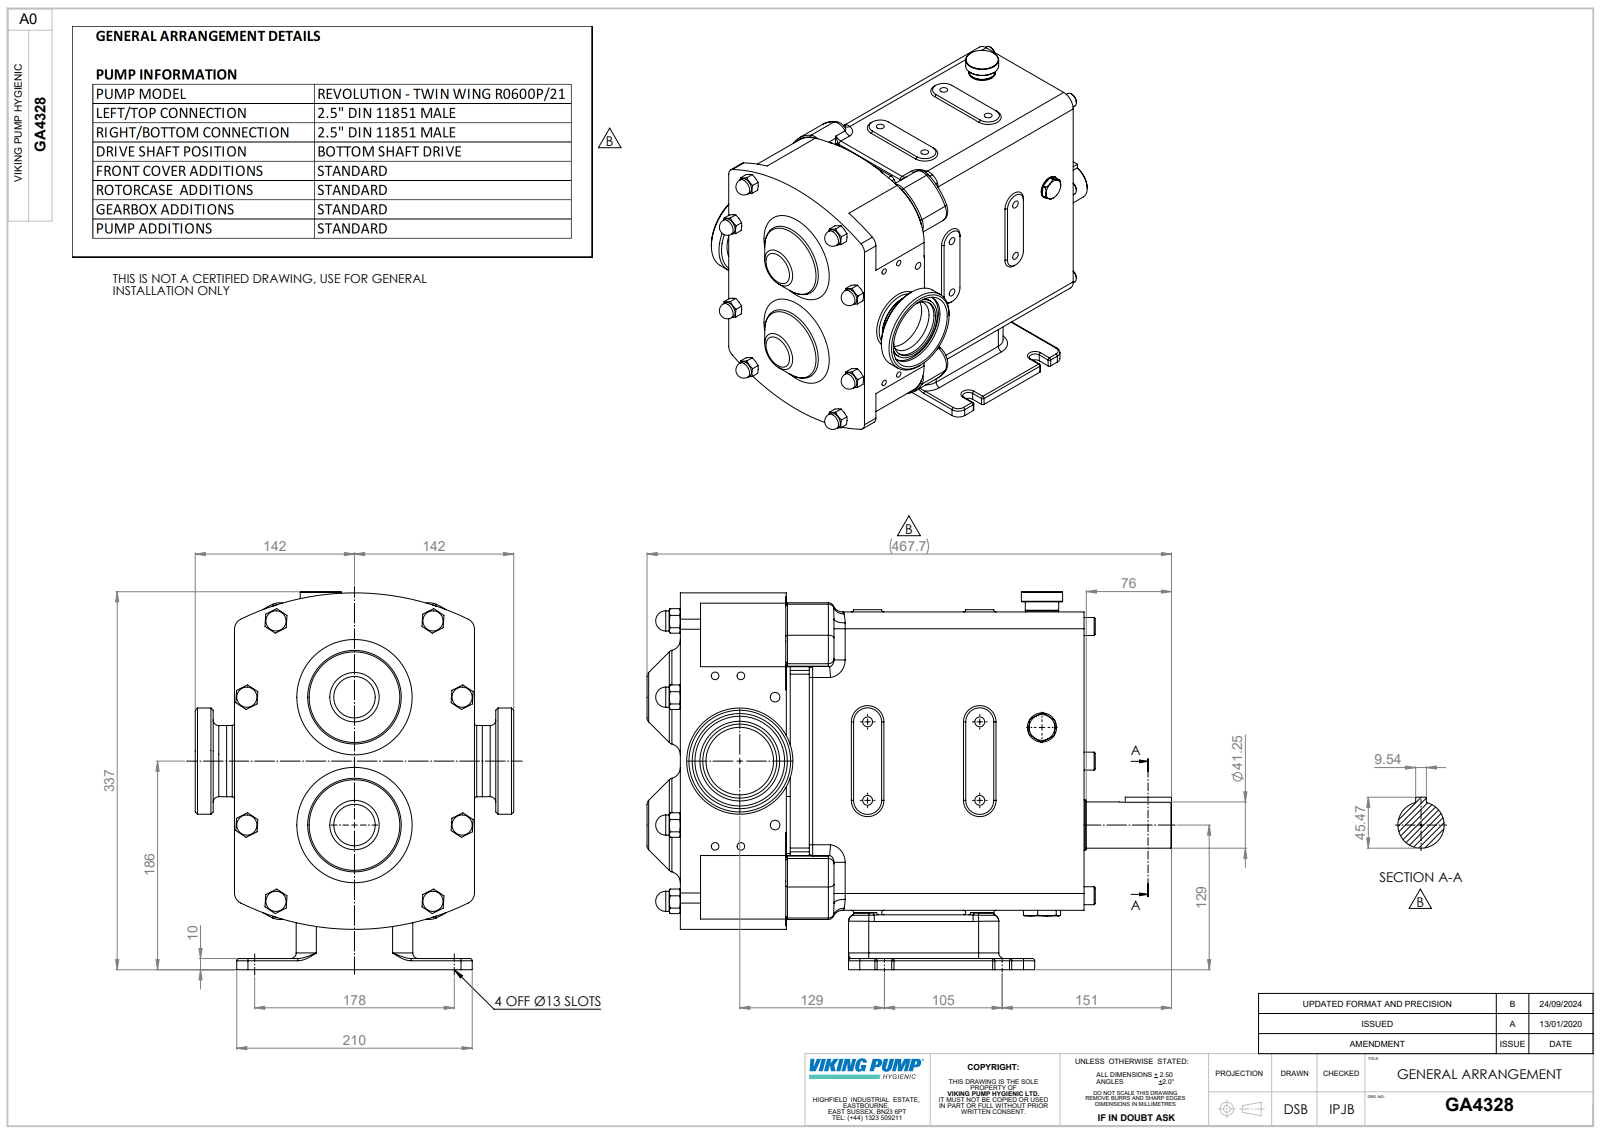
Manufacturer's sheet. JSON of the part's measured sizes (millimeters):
{"part_name": "GA4328; Copy of R0600 CPP H BSD^GA4328; Copy of Z94-5031-44 - 2.5 INCH DIN11851^GA4328", "step_written_by": "SolidWorks 2023 (AUTOMOTIVE_DESIGN)", "units": "millimeters", "bodies": {"solids": 3, "faces": 940, "planar": 292, "cylindrical": 285, "other": 363}, "overall_size": [467.7, 337, 284], "volume_mm3": 17310000, "surface_area_mm2": 699861, "round_holes": [[8.8, 8], [6.8, 4], [8.6, 2], [33.8, 1], [60.3, 1], [66, 1], [80, 1]], "round_bosses_or_shafts": [[18, 8], [16, 6], [94.7, 1], [71.1, 1], [63.6, 1], [63.4, 1], [51, 1], [45, 1]], "partial_cylinders_radius": [[2, 38], [10, 30], [5, 19], [5.9, 8], [15, 8], [18, 8], [3, 4], [6, 4]], "face_to_face_distances": [152, 94.5, 265.5, 360, 3.5, 262, 98, 43, 266, 183], "hole_center_spacings": [70, 100, 122.07, 23, 35.93, 56.77, 65.12, 76.01]}
